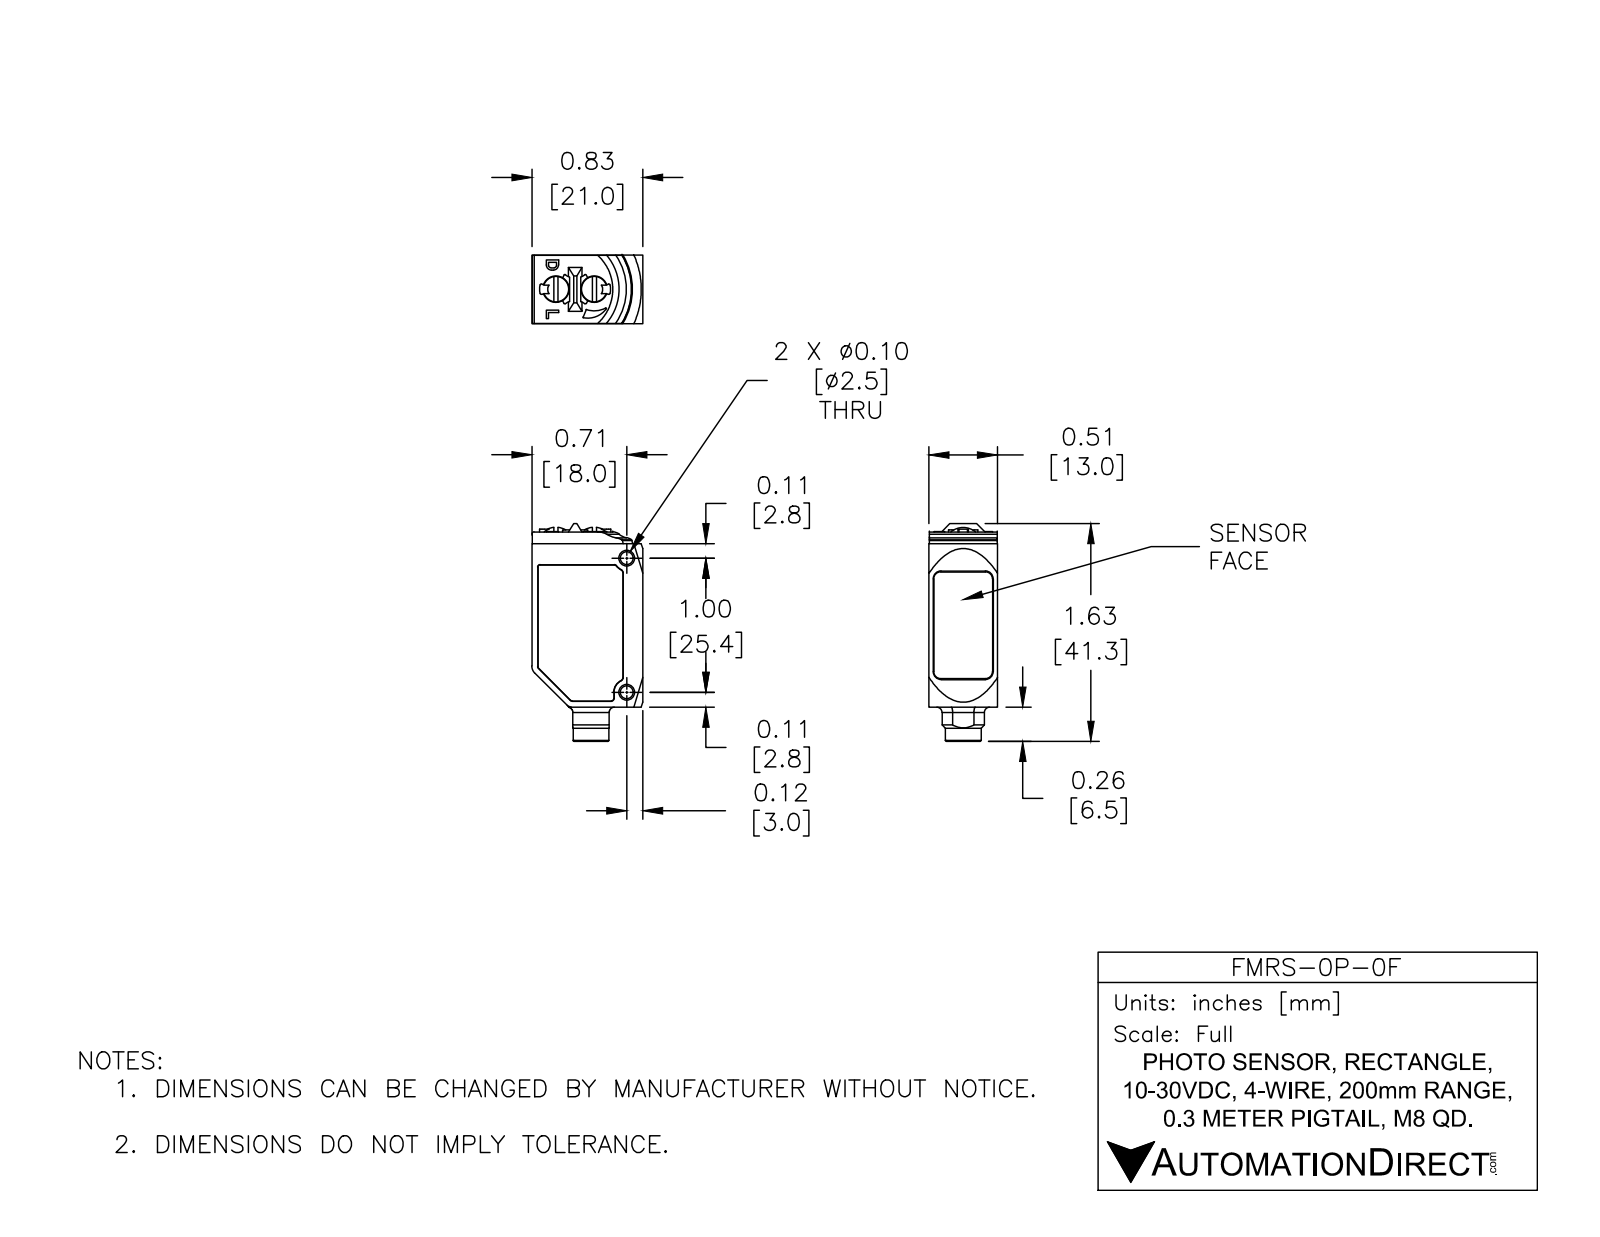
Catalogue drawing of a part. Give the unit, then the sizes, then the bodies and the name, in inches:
Units: inches
Overall size (bounding box): 1.626 × 0.827 × 0.512
Round holes (diameter × count): ⌀0.097 ×2, ⌀0.197 ×2, ⌀0.228 ×1
Round bosses / shafts (diameter × count): ⌀0.189 ×2, ⌀0.267 ×1
Partial cylindrical surfaces — rounded edges, fillets, slot ends (radius × count): R0.018 ×7, R0.02 ×7, R0.039 ×5, R0.008 ×4, R0.01 ×4, R0.051 ×4, R0.059 ×4, R0.004 ×3
Main face-to-face distances: 0.512, 0.827, 1.307, 0.51, 0.031, 0.48, 0.037, 0.035, 0.474, 0.03
Hole centre spacings: 0.026, 0.262, 0.287, 1
Volume: 0.527 in³ · Surface area: 5.26 in²
Bodies: 1 solid, 197 faces (89 planar, 79 cylindrical, 29 other)
Part name (STEP PRODUCT): FMRS-0P-0F
STEP written by: SolidWorks 2017 (AUTOMOTIVE_DESIGN)
